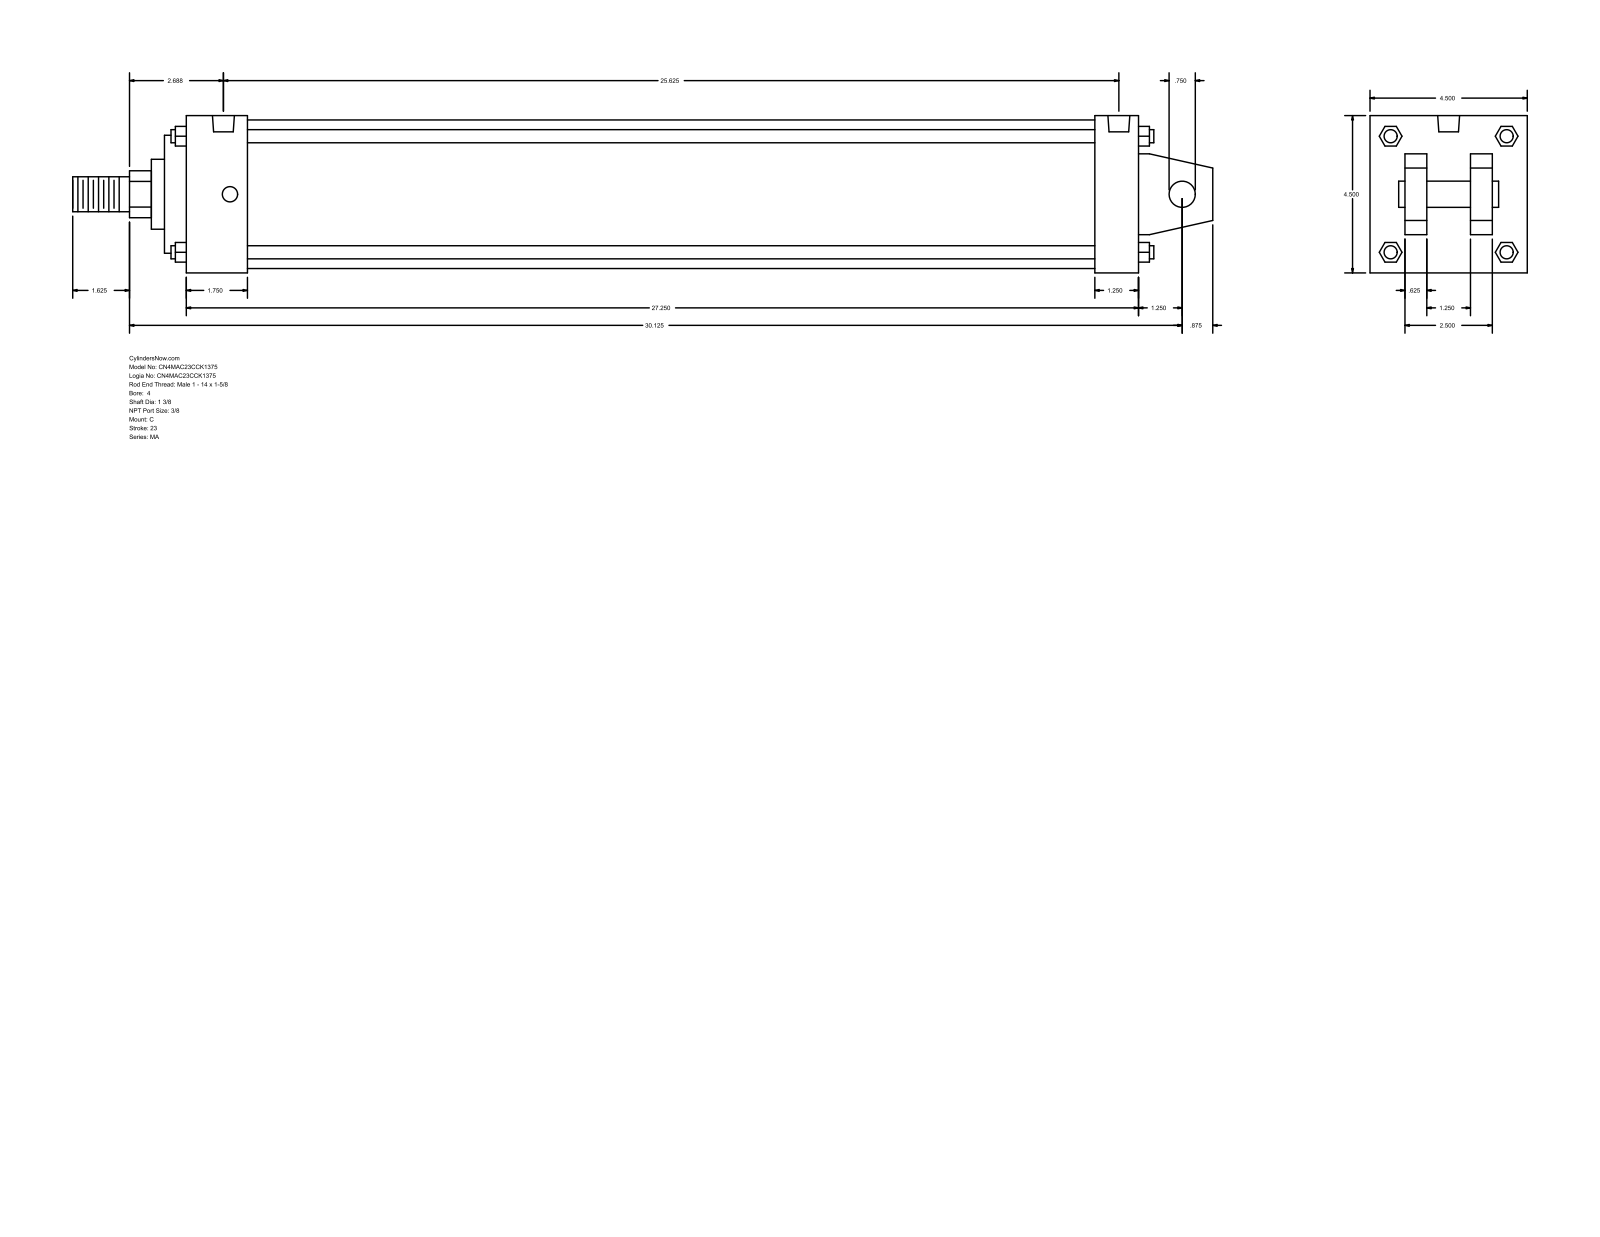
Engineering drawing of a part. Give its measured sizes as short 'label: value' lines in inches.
name: MA_C__0400_1.375
written by: GSSL Pune (CONFIG_CONTROL_DESIGN)
unit: in
bodies: 0 solids, 141 faces (109 planar, 32 cylindrical, 0 other)
size: 32.625 × 4.5 × 4.5
holes: 4× ⌀0.437, 2× ⌀0.627
bosses: 4× ⌀0.375, 1× ⌀4.25, 1× ⌀3.375, 1× ⌀2, 1× ⌀1.375, 1× ⌀1, 1× ⌀0.75
rounds: 1× R0.672
face distances: 4.5, 0.625, 27.25, 2.875, 1.625, 1, 3.5, 1.875, 27.875, 26.625
hole spacings: 25.25, 0.187, 0.188, 25.437, 25.438, 25.625
